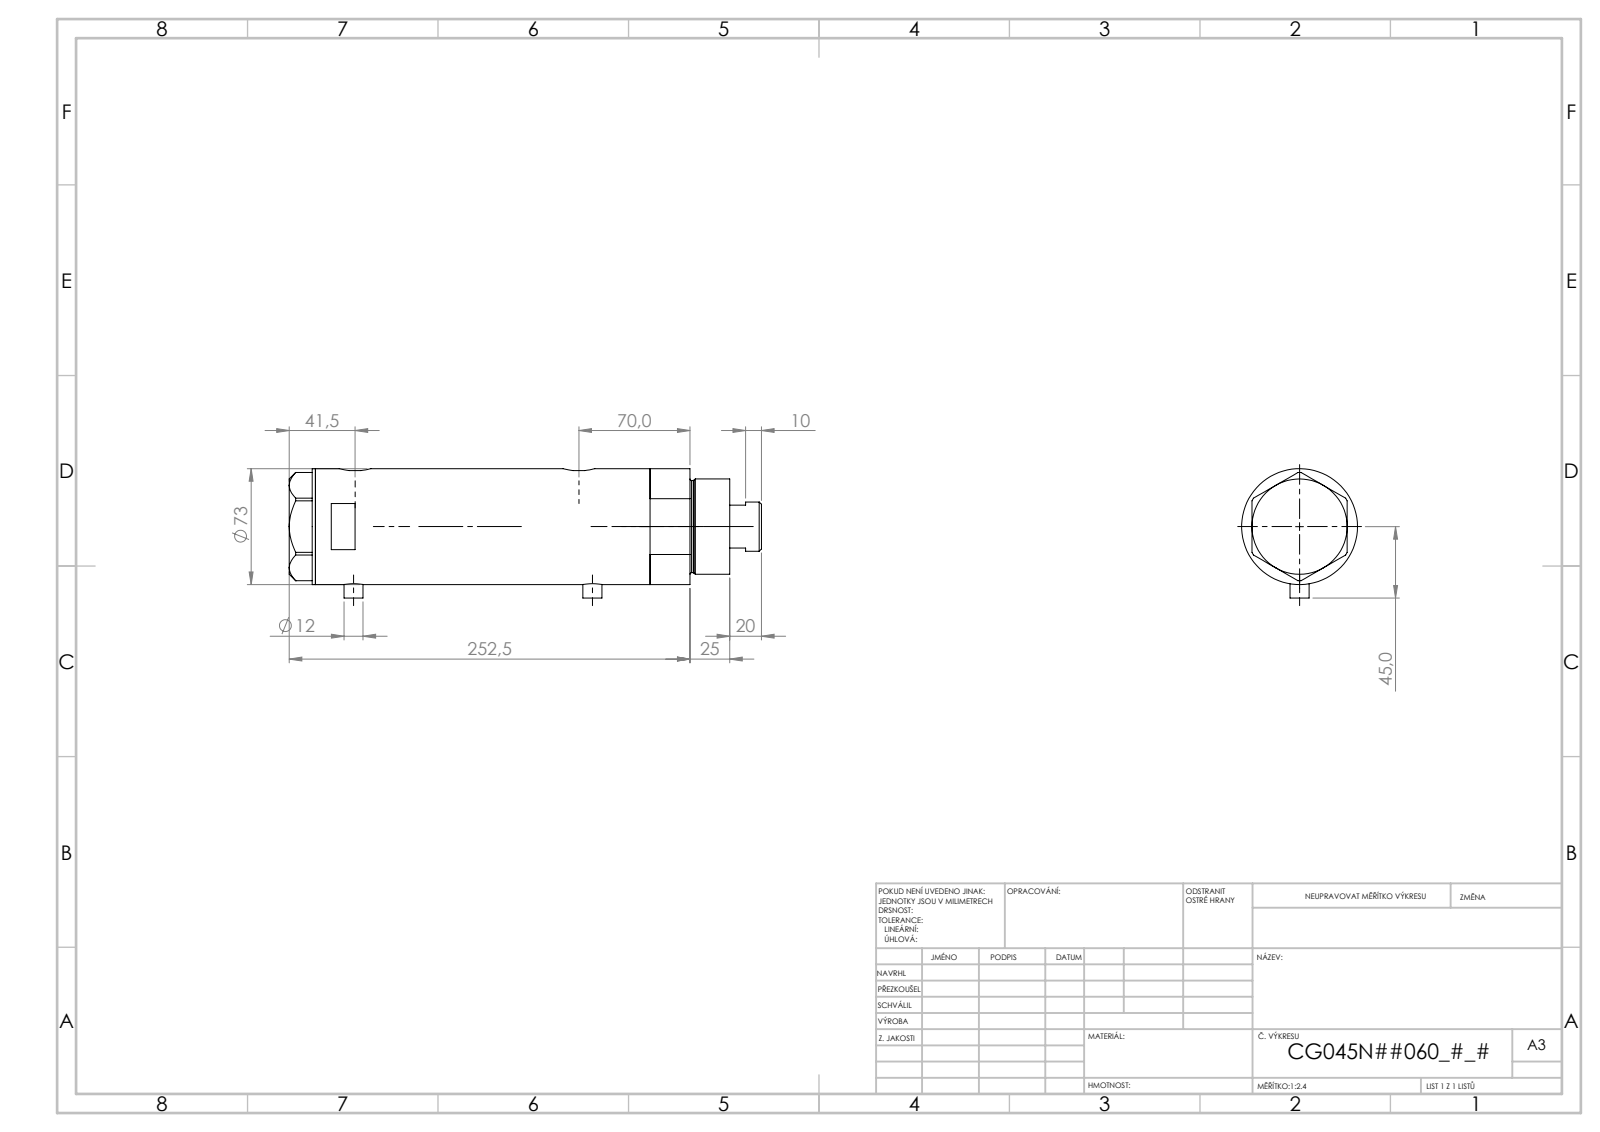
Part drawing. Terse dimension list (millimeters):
name: V270CG_FRONT; V270CG_VC; V270CG_MIDDLE; V270CG_BACK
written by: SolidWorks 2019 (CONFIG_CONTROL_DESIGN)
unit: mm
bodies: 4 solids, 125 faces (50 planar, 55 cylindrical, 20 other)
size: 251.52 × 74.1 × 73
volume: 870 708 mm³; area: 148 215 mm²
holes: 2× ⌀5, 2× ⌀12.5, 2× ⌀13.16, 1× ⌀10.5, 1× ⌀32, 1× ⌀33.5, 1× ⌀45, 1× ⌀48, 1× ⌀64
bosses: 2× ⌀12, 1× ⌀73, 1× ⌀60, 1× ⌀58, 1× ⌀31
rounds: 2× R10
face distances: 127.14, 16.5, 143.64, 60, 215.01, 231.51, 87.87, 42.5, 26, 101.14
hole spacings: 111.65, 0.99, 1, 8.5, 8.51, 102.15, 103.14, 103.15
